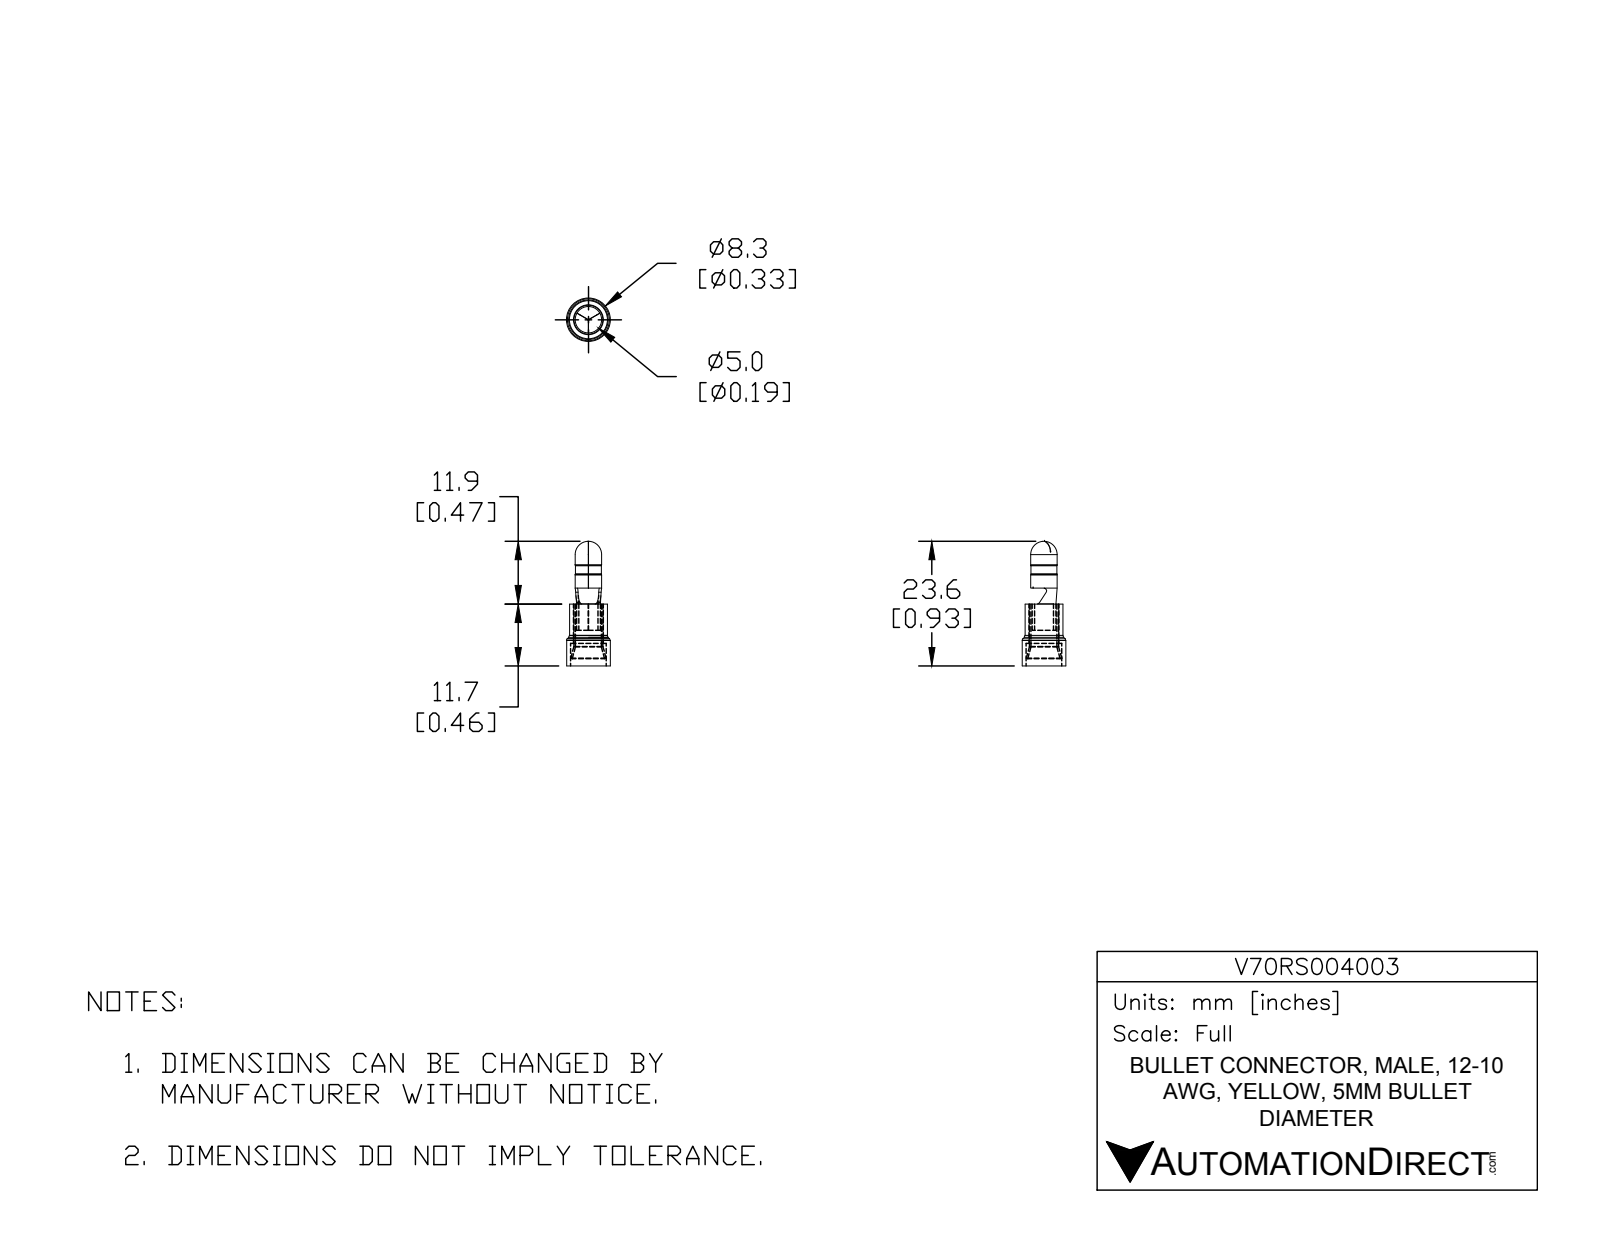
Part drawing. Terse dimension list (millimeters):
name: V70RS004003
written by: SolidWorks 2017 (AUTOMOTIVE_DESIGN)
unit: mm
bodies: 3 solids, 96 faces (24 planar, 34 cylindrical, 38 other)
size: 23.58 × 8.26 × 8.26
volume: 346 mm³; area: 1 359 mm²
holes: 1× ⌀3.6, 1× ⌀4.1, 1× ⌀5.66, 1× ⌀6.76
bosses: 1× ⌀8.26, 1× ⌀7.16, 1× ⌀5.5, 1× ⌀5, 1× ⌀4.9, 1× ⌀4.5
rounds: 2× R0.5
face distances: 11.72, 4.25, 7.47, 6.72, 2.47, 5, 14.72, 10.47, 8, 3
